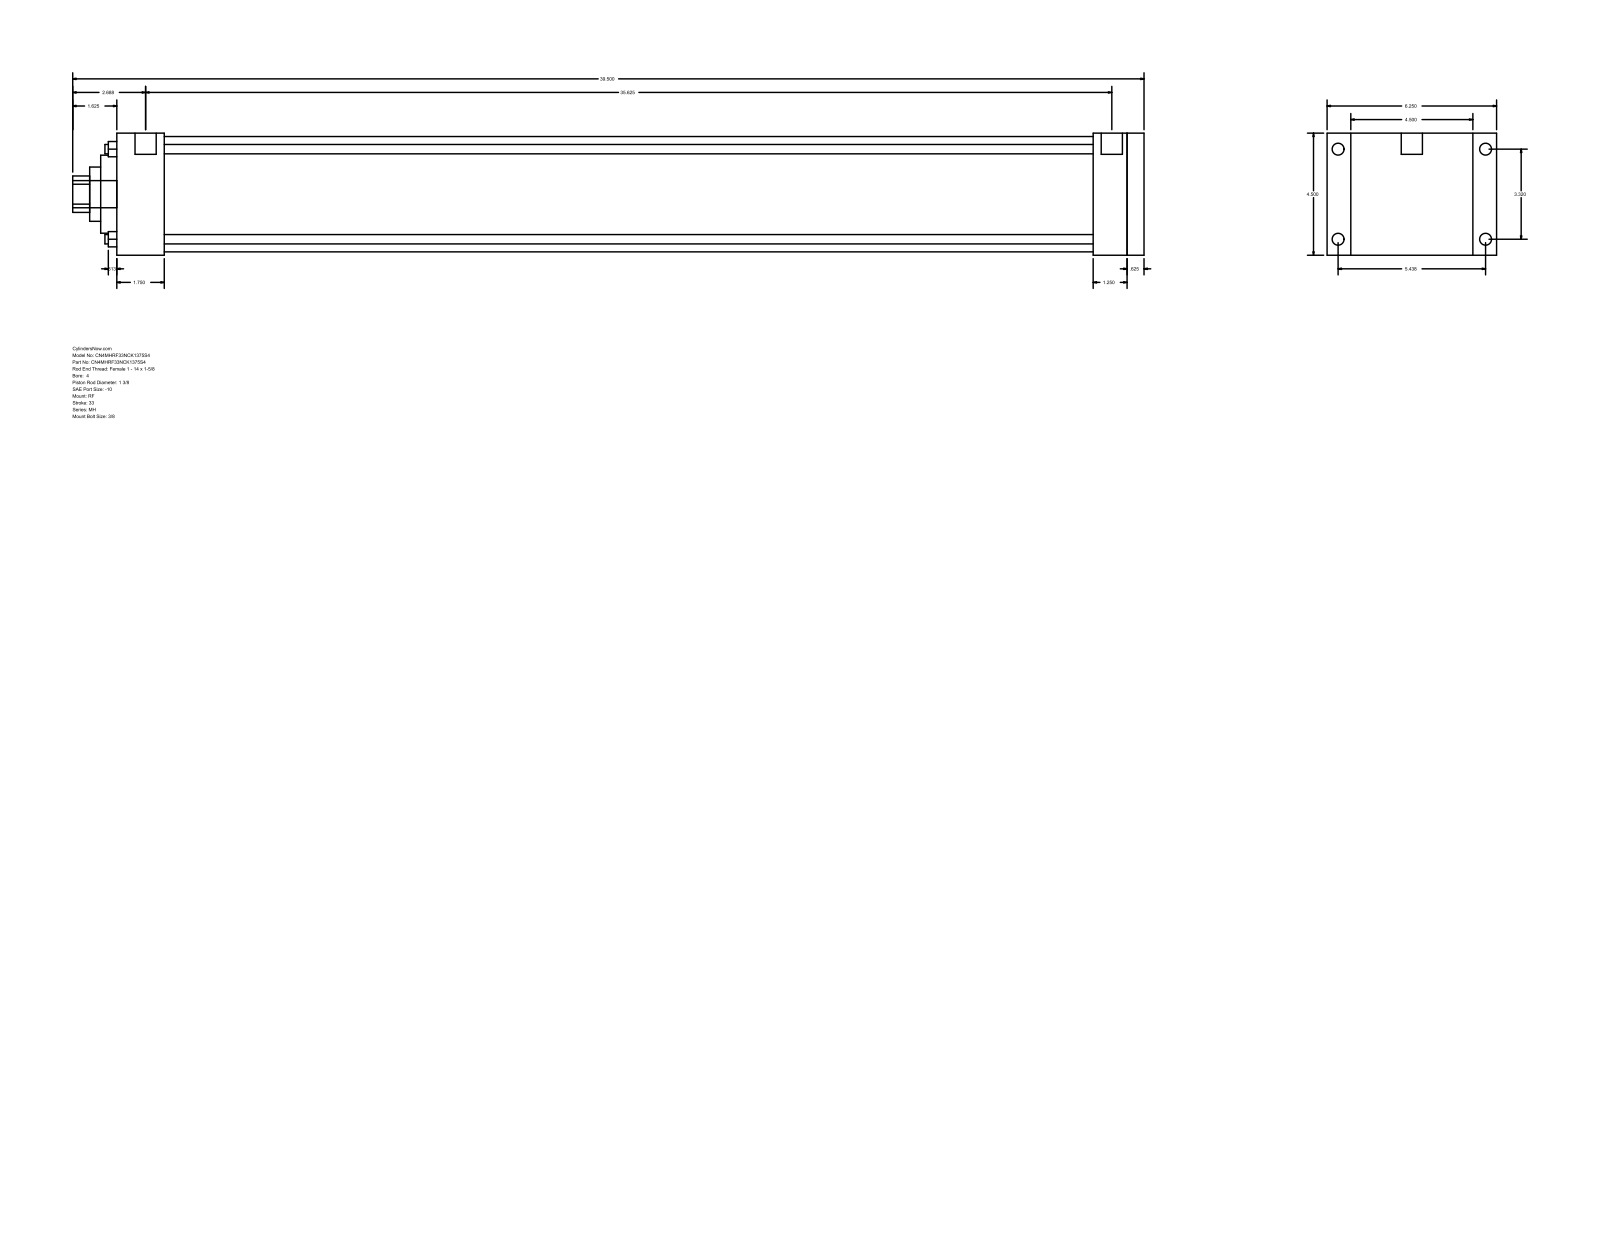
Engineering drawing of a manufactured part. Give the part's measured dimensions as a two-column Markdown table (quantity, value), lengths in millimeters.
| quantity | value |
| --- | --- |
| part name | MH_RF__0400_1.375 |
| STEP written by | GSSL Pune (CONFIG_CONTROL_DESIGN) |
| units | millimeters |
| bodies | 0 solids, 94 faces (65 planar, 29 cylindrical, 0 other) |
| overall size | 1003.3 × 158.75 × 114.3 |
| round holes (diameter × count) | 8.76 × 4, 34.92 × 1, 50.8 × 1, 73.03 × 1, 107.95 × 1 |
| round bosses / shafts (diameter × count) | 11.13 × 4, 8.73 × 4, 19.84 × 2, 25.4 × 1 |
| partial cylindrical surfaces (radius × count) | 17.06 × 1 |
| main face-to-face distances | 114.3, 962.03, 15.88, 946.15, 44.45, 901.7, 917.58, 914.4, 869.95, 31.75 |
| hole center spacings | 59.62, 84.32, 119.25 |
